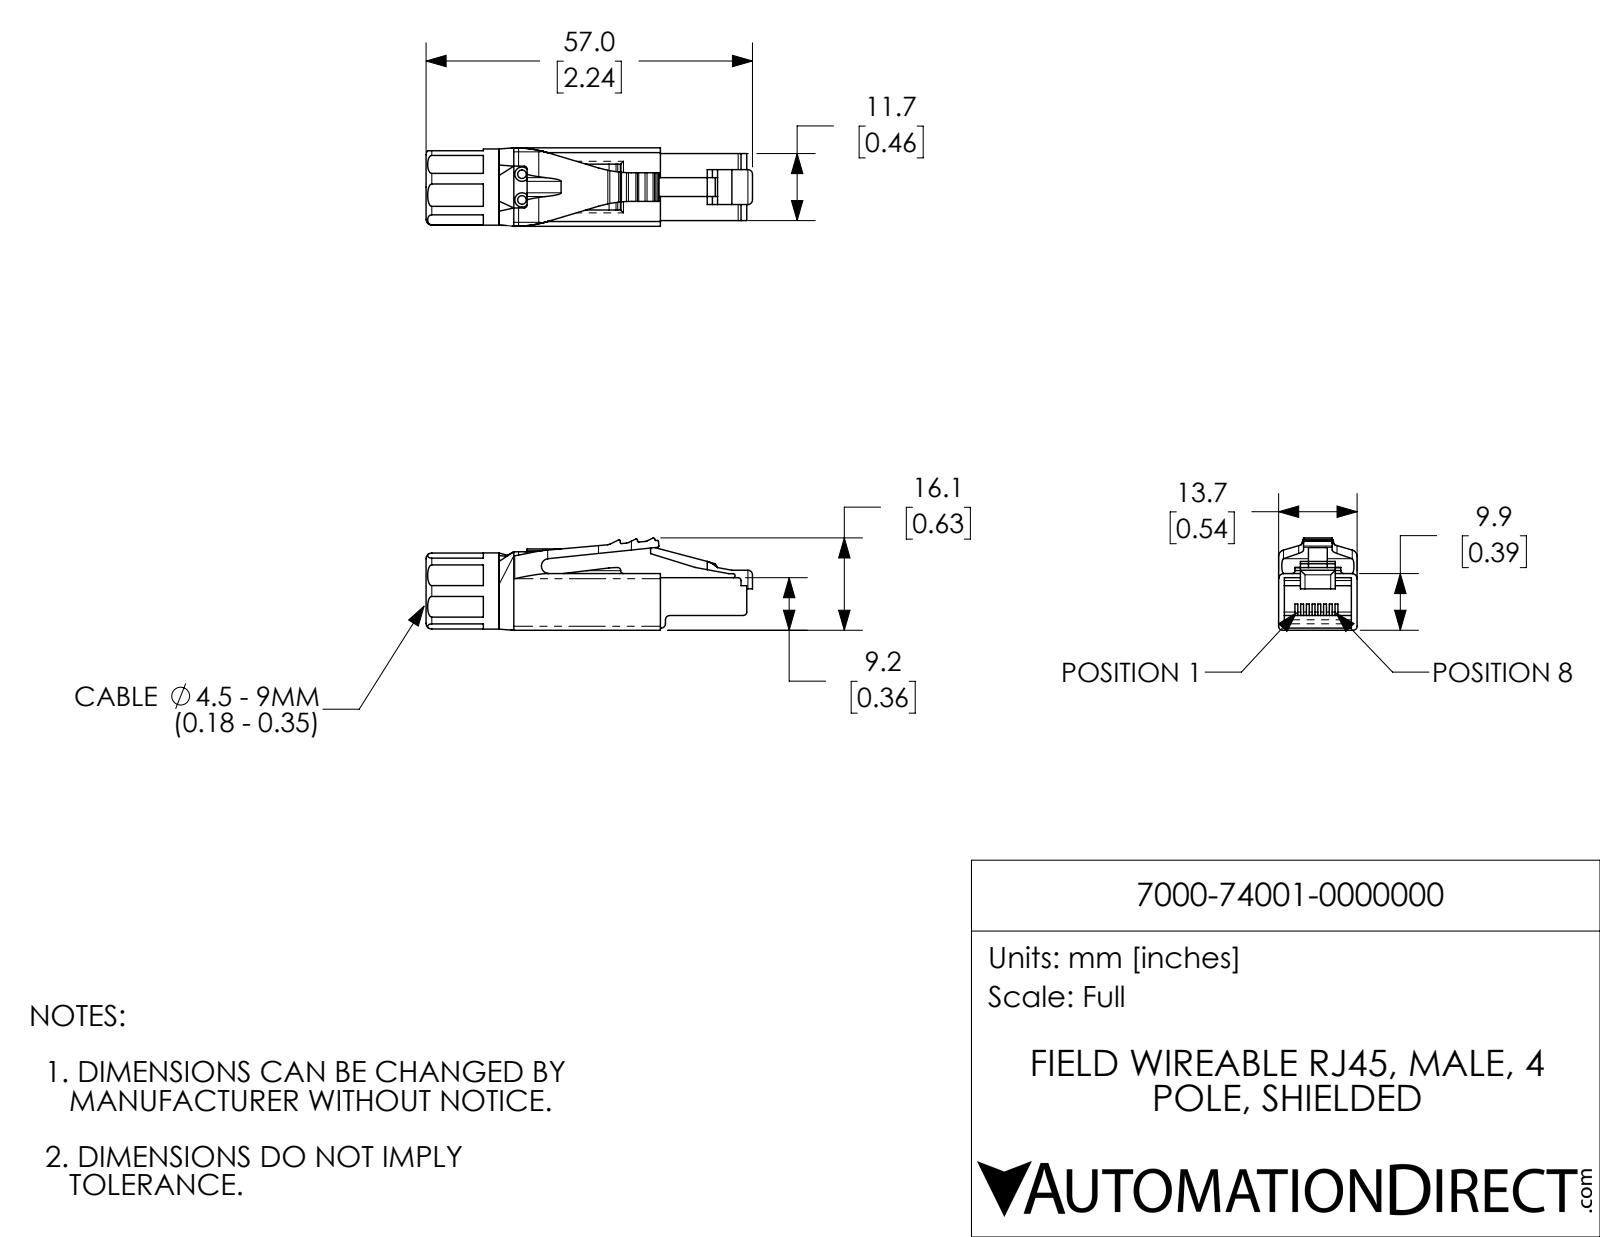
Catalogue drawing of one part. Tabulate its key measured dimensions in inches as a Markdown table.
| quantity | value |
| --- | --- |
| part name | 7000-74001-0000000 |
| STEP written by | SolidWorks 2017 (AUTOMOTIVE_DESIGN) |
| units | inches |
| bodies | 2 solids, 206 faces (124 planar, 69 cylindrical, 13 other) |
| overall size | 2.244 × 0.635 × 0.539 |
| volume | 0.395 in³ |
| surface area | 6.357 in² |
| round holes (diameter × count) | 0.059 × 2, 0.378 × 1 |
| round bosses / shafts (diameter × count) | 0.524 × 1 |
| partial cylindrical surfaces (radius × count) | 0.008 × 8, 0.02 × 7, 0.039 × 7, 0.069 × 6, 0.028 × 4, 0.031 × 3, 0.03 × 2, 0.035 × 2 |
| main face-to-face distances | 0.039, 0.5, 0.539, 0.361, 0.102, 0.26, 0.389, 0.288, 0.028, 0.461 |
| hole center spacings | 0.177 |
